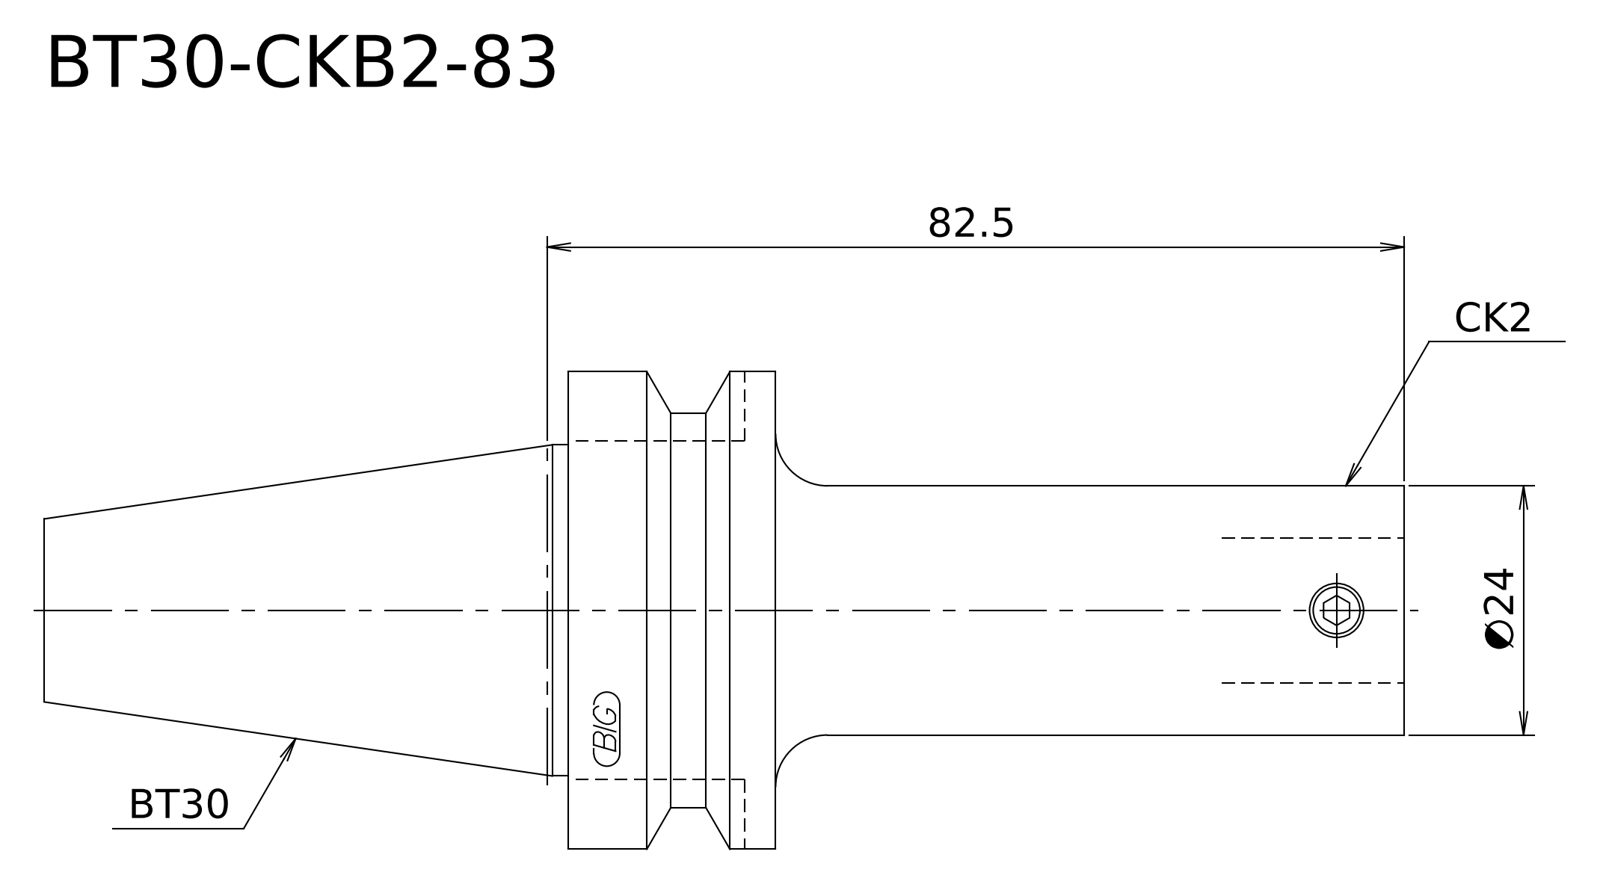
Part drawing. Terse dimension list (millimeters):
written by: Kubotek KeyCreator V8.5.1 (14335) (CONFIG_CONTROL_DESIGN)
unit: mm
bodies: 1 solid, 13 faces (4 planar, 5 cylindrical, 4 other)
size: 130.9 × 46 × 46
volume: 84 042 mm³; area: 14 494 mm²
bosses: 1× ⌀46, 1× ⌀38, 1× ⌀31.9, 1× ⌀24
face distances: 20, 60.5, 80.5, 130.9, 70.4, 50.4
